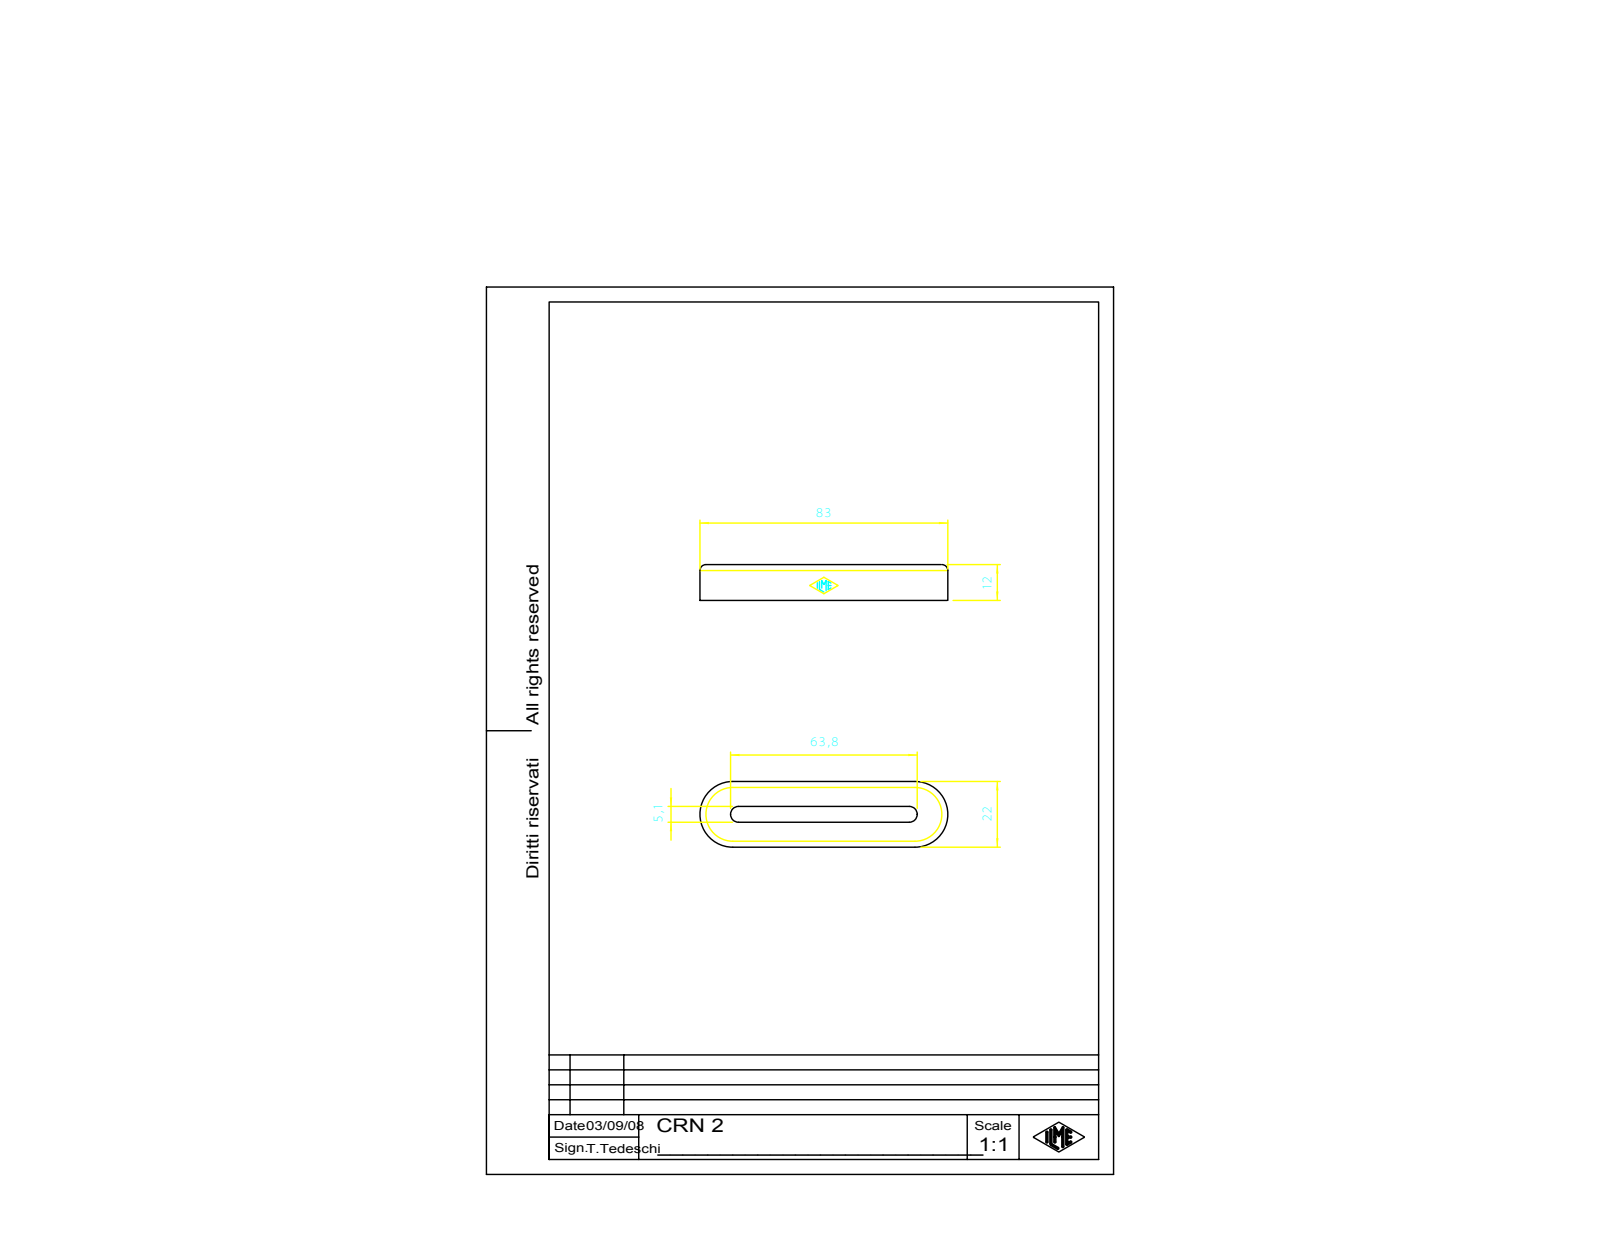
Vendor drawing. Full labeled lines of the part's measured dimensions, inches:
Part name (STEP PRODUCT): CRN_2
STEP written by: OneSpace Modeling 15.50B 03-Nov-2007 (C) CoCreate Software GmbH (AUTOMOTIVE_DESIGN)
Units: inches
Bodies: 1 solid, 84 faces (43 planar, 37 cylindrical, 4 other)
Overall size (bounding box): 3.268 × 0.866 × 0.472
Volume: 1.013 in³ · Surface area: 10.16 in²
Partial cylindrical surfaces — rounded edges, fillets, slot ends (radius × count): R0.005 ×11, R0.079 ×2, R0.104 ×2, R0.433 ×2, R0.008 ×1, R0.008 ×1, R0.01 ×1
Main face-to-face distances: 0.329, 0.537, 0.472, 0.209, 0.866, 0.039, 0.134, 0.02, 0.14, 0.059
